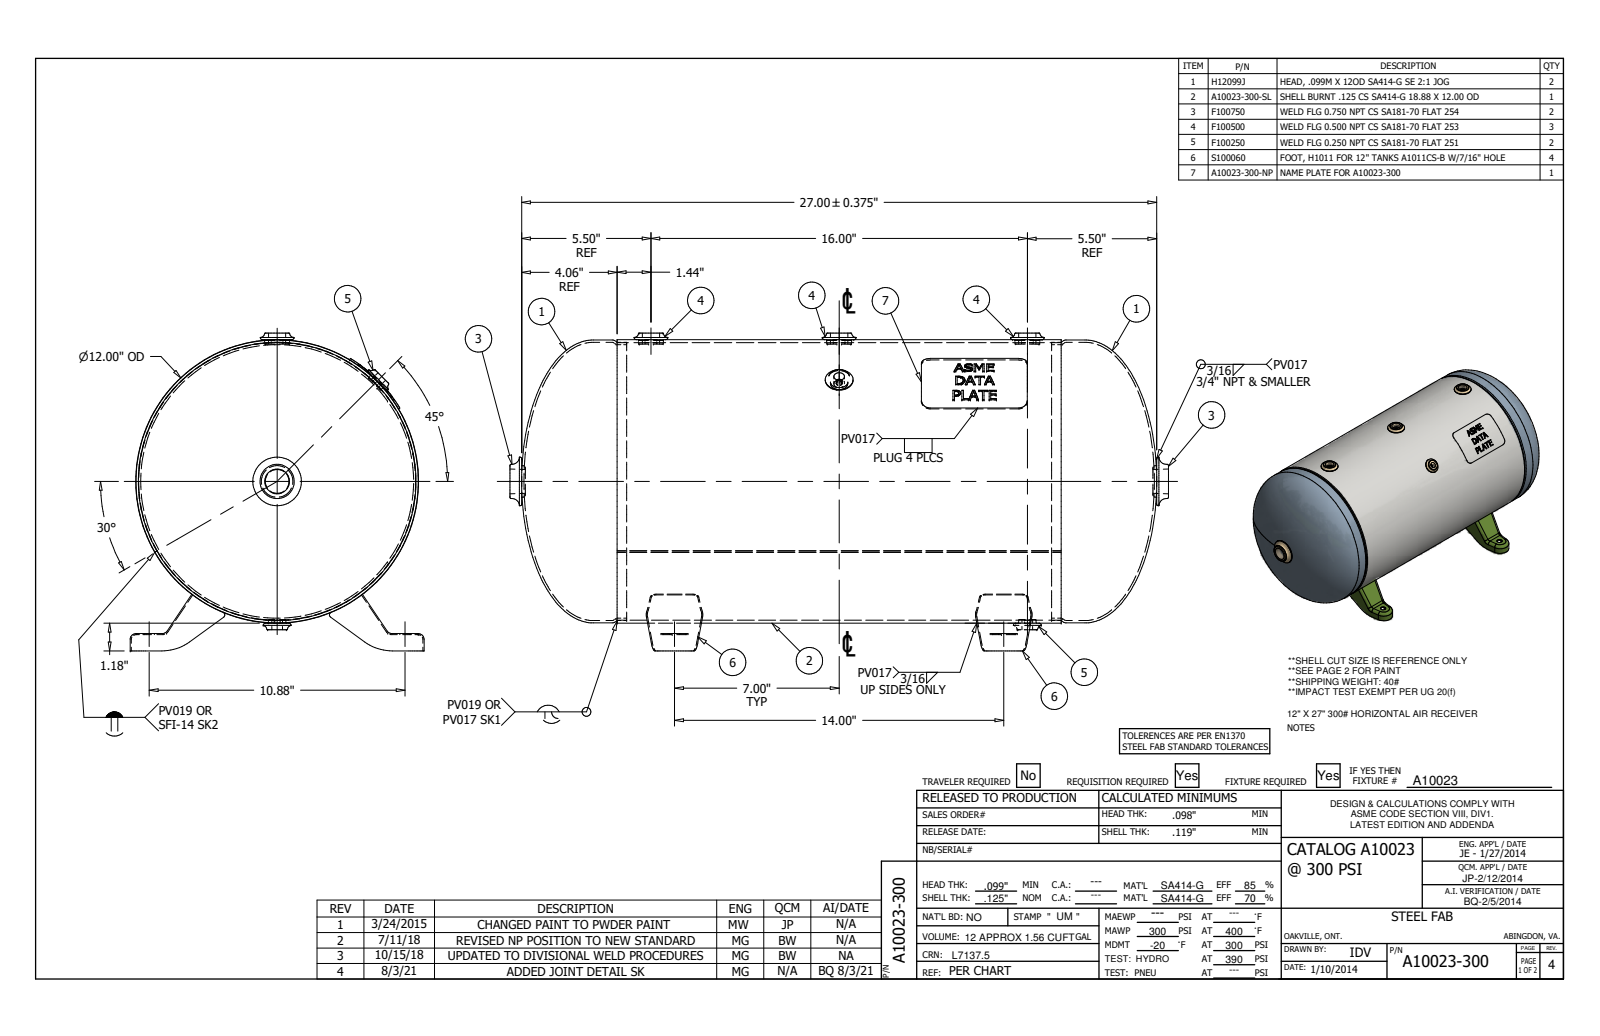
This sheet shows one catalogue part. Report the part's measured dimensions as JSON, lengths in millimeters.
{"part_name": "A10023-300; A10023-300-SL; H12099J; F100750 (+4 more)", "step_written_by": "Autodesk Inventor 2017 (AUTOMOTIVE_DESIGN)", "units": "millimeters", "bodies": {"solids": 15, "faces": 439, "planar": 195, "cylindrical": 123, "other": 121}, "overall_size": [711.3, 342.39, 317.5], "volume_mm3": 2228000, "surface_area_mm2": 1575000, "round_holes": [[11.11, 4], [12.7, 3], [18.64, 3], [6.35, 2], [11.46, 2], [294.69, 1], [299.01, 1], [299.77, 1], [304.8, 1]], "round_bosses_or_shafts": [[26.99, 3], [305.36, 1], [299.72, 1], [52.39, 1], [36.91, 1]], "partial_cylinders_radius": [[6.35, 18], [5.15, 16], [9.53, 4], [17.85, 4], [19.05, 4], [3.17, 2], [7.55, 2], [50.8, 2]], "face_to_face_distances": [1.2, 352.4, 74.38, 353.6, 351.2, 74.34, 1.21, 10.34, 469.22, 75.54], "hole_center_spacings": [140.44, 225.14, 405.32, 203.26, 276.22, 355.6, 405.31, 450.28]}
